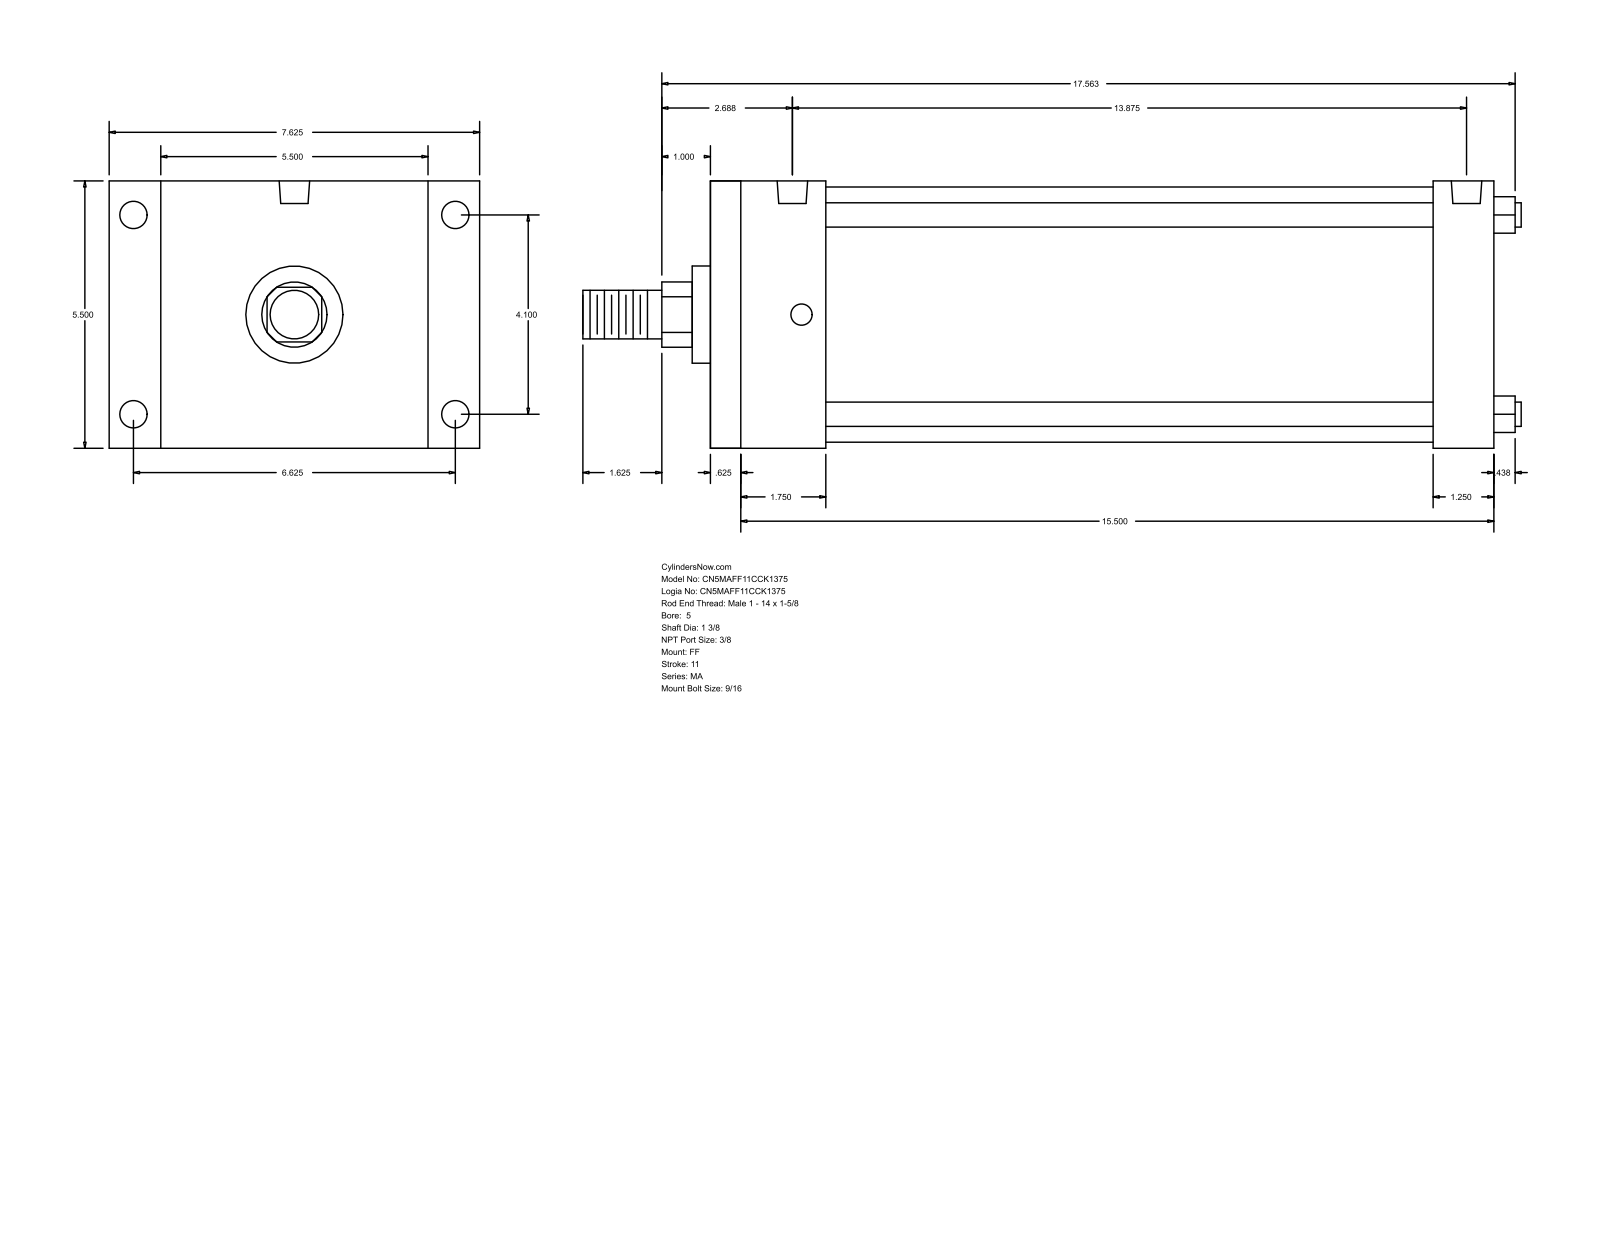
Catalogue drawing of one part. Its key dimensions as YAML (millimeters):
part_name: "MA_FF__0500_1.375"
step_written_by: "GSSL Pune (CONFIG_CONTROL_DESIGN)"
units: millimeters
bodies: {solids: 0, faces: 92, planar: 64, cylindrical: 28, other: 0}
overall_size: [490.54, 193.68, 139.7]
round_holes:
  - {diameter: 11.11, count: 4}
  - {diameter: 14.29, count: 4}
  - {diameter: 15.93, count: 2}
round_bosses_or_shafts:
  - {diameter: 12.7, count: 4}
  - {diameter: 133.35, count: 1}
  - {diameter: 50.8, count: 1}
  - {diameter: 34.92, count: 1}
  - {diameter: 25.4, count: 1}
partial_cylinders:
  - {radius: 17.06, count: 1}
face_to_face_distances: [139.7, 409.58, 15.87, 393.71, 377.83, 361.96, 31.75, 60.32, 44.45, 317.51]
hole_center_spacings: [104.14, 168.28, 197.9, 342.9, 4.76, 4.77, 347.66, 347.67]
